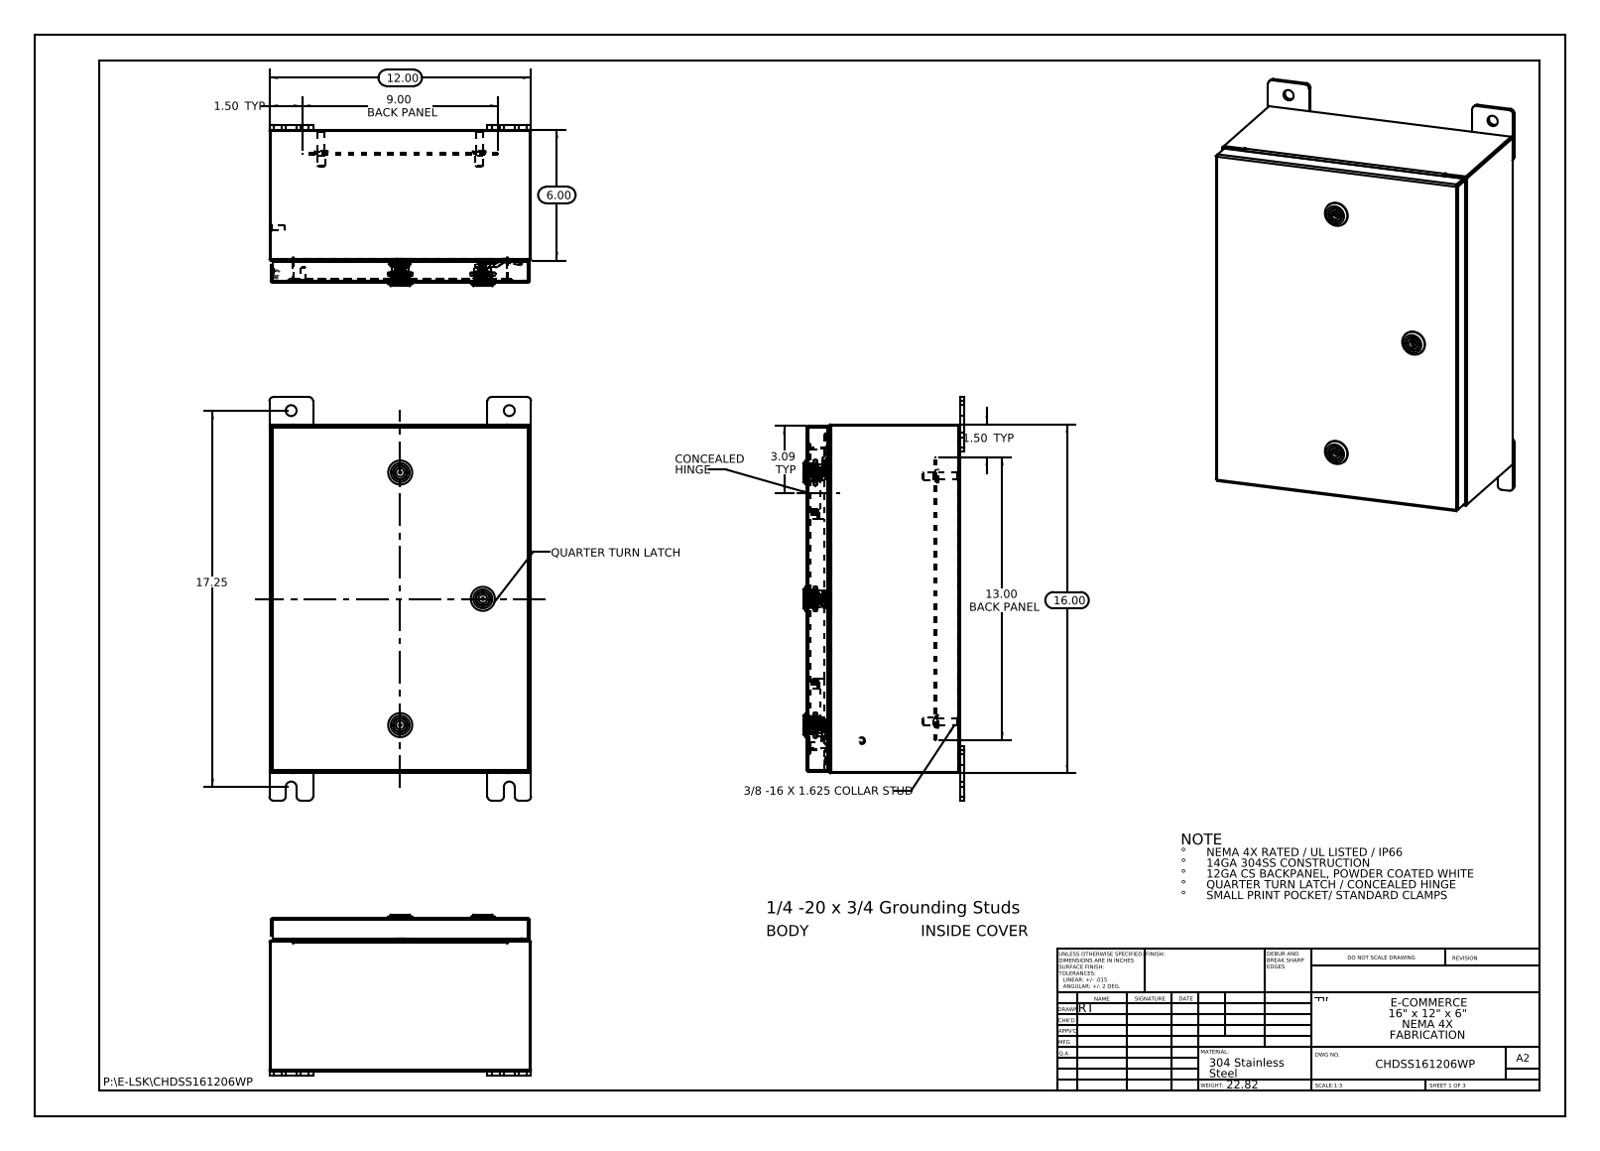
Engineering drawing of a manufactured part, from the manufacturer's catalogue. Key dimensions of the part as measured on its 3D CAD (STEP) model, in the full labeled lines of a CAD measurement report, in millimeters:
Part name (STEP PRODUCT): HW-CLH-R001-0500_2412-026240-2445-Industrilas; CHDSS161206WP; HW-CLH-E5-8004_Cam-232112-U-Industrilas; CHDSS161206WP Mounting Studs (+8 more)
STEP written by: SolidWorks 2013 (CONFIG_CONTROL_DESIGN)
Units: millimetres
Bodies: 35 solids, 2902 faces (898 planar, 906 cylindrical, 1098 other)
Overall size (bounding box): 469.9 × 304.8 × 187.1
Volume: 1 345 000 mm³ · Surface area: 1 333 000 mm²
Round holes (diameter × count): ⌀12.7 ×8, ⌀5 ×3, ⌀10 ×3, ⌀10.2 ×3, ⌀16 ×3, ⌀20 ×3, ⌀5.4 ×1
Round bosses / shafts (diameter × count): ⌀6 ×5, ⌀15.9 ×4, ⌀9.5 ×4, ⌀8.4 ×4, ⌀28 ×3, ⌀19.8 ×3, ⌀15.9 ×3, ⌀15.5 ×3
Partial cylindrical surfaces — rounded edges, fillets, slot ends (radius × count): R0.2 ×99, R3 ×99, R0.7 ×36, R4.8 ×24, R0.3 ×18, R2.2 ×18, R0.5 ×12, R5 ×12
Main face-to-face distances: 1.9, 1.9, 302.9, 178.3, 176.4, 176.4, 174.5, 404.5, 25.4, 27.3
Hole centre spacings: 304.2, 56.5, 83.8, 92.2, 92.2, 133.2, 143, 146
